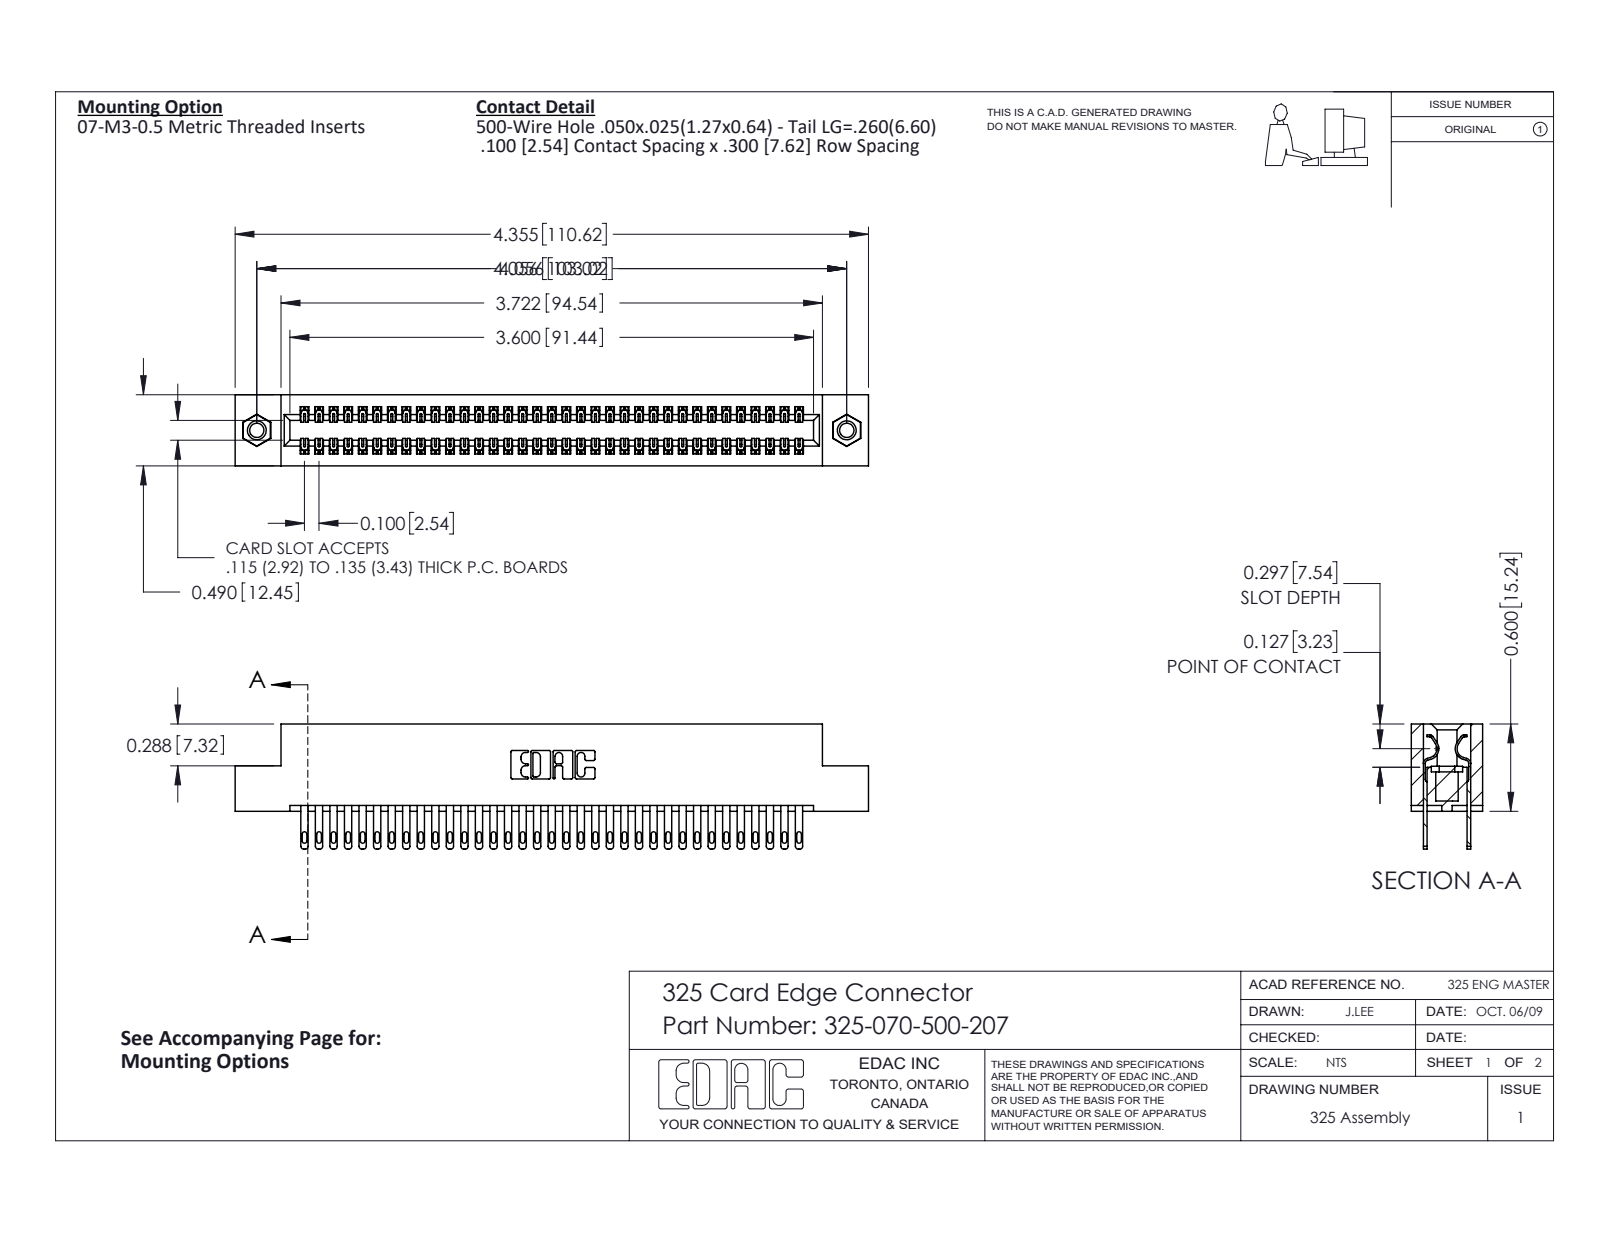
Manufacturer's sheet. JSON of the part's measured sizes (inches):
{"part_name": "345-250-001_345-250-005-103; 325-070-500-207; 325-292-001_325-293-100; 325 Part_TI", "step_written_by": "SolidWorks 2016 (CONFIG_CONTROL_DESIGN)", "units": "inches", "bodies": {"solids": 73, "faces": 3534, "planar": 2202, "cylindrical": 1316, "other": 16}, "overall_size": [4.355, 0.86, 0.49], "volume_in3": 0.88, "surface_area_in2": 27.97, "round_holes": [[0.098, 2], [0.125, 2], [0.16, 2]], "round_bosses_or_shafts": [[0.155, 2]], "partial_cylinders_radius": [[0.006, 105], [0.016, 70], [0.02, 70], [0.01, 22], [0.007, 6], [0.031, 6], [0.026, 3], [0.014, 2]], "face_to_face_distances": [0.083, 0.407, 0.3, 0.107, 0.383, 0.025, 0.49, 0.325, 0.275, 0.56], "hole_center_spacings": [4.056]}
